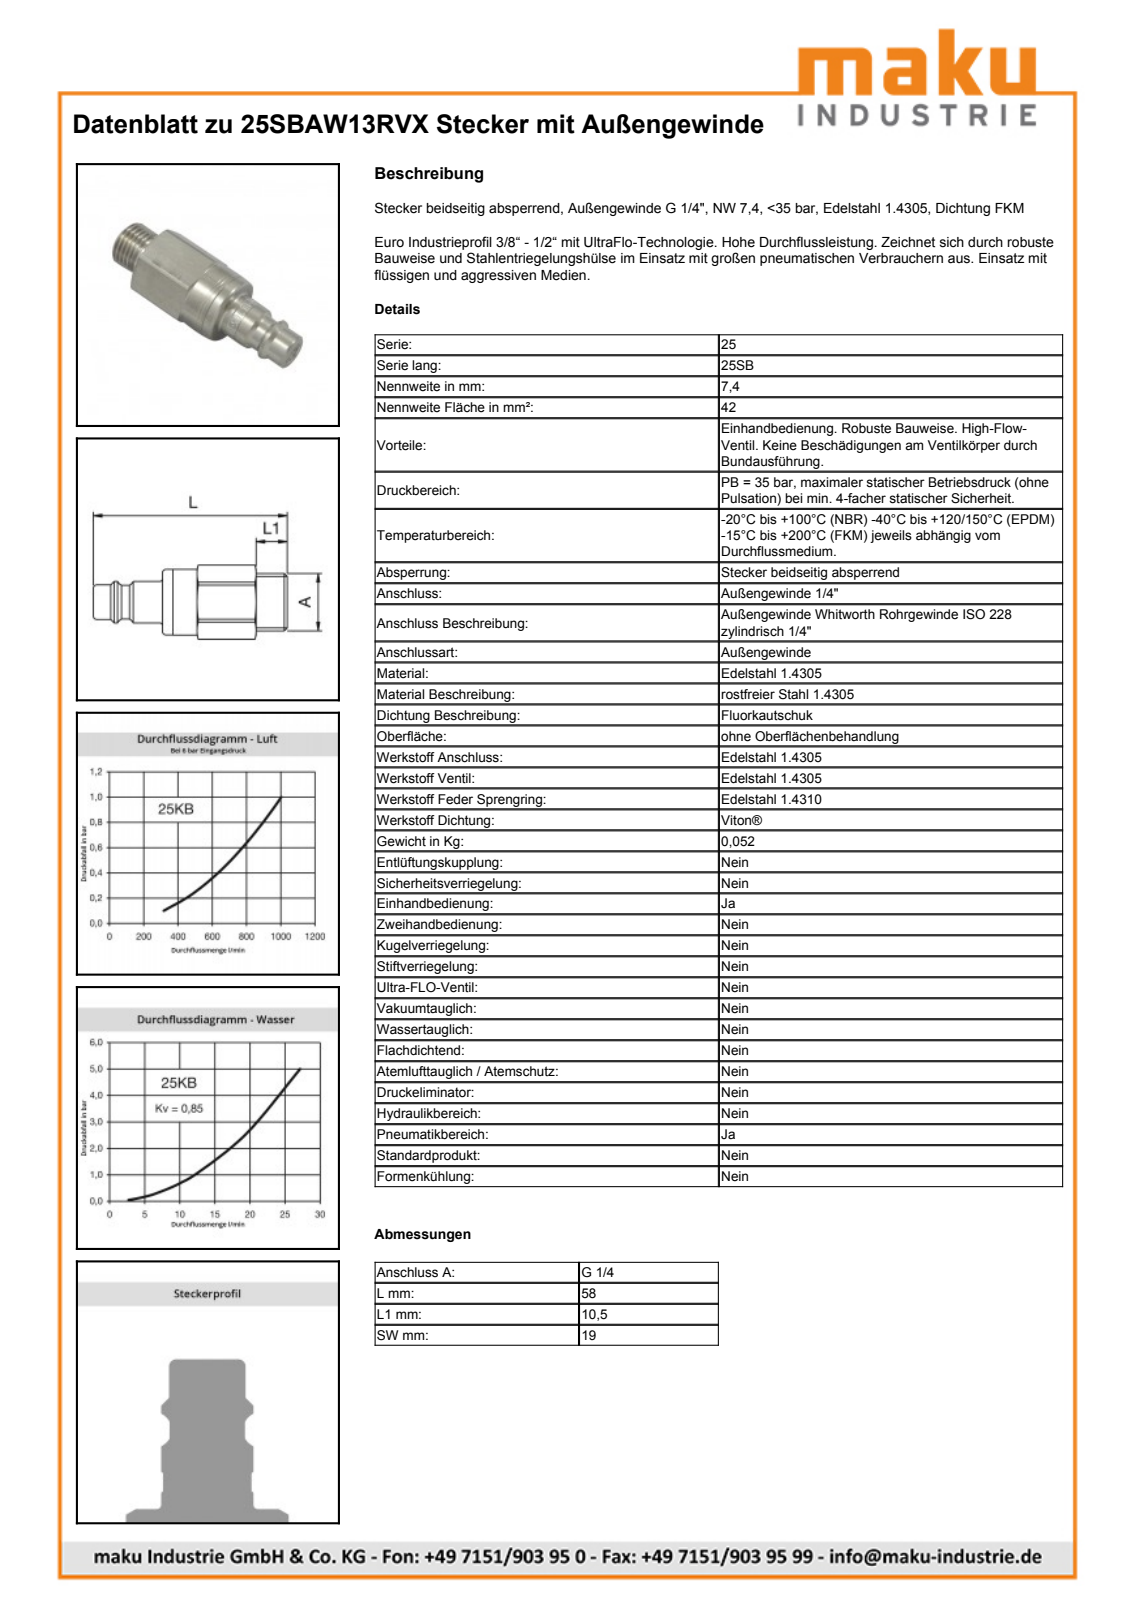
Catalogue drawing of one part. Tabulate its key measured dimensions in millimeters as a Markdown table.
| quantity | value |
| --- | --- |
| part name | D107955 |
| STEP written by | Autodesk Inventor 2013 (AUTOMOTIVE_DESIGN) |
| units | millimeters |
| bodies | 1 solid, 56 faces (16 planar, 19 cylindrical, 21 other) |
| overall size | 58 × 20.96 × 20.84 |
| volume | 11 382 mm³ |
| surface area | 4 196 mm² |
| round holes (diameter × count) | 15.1 × 1, 16 × 1 |
| round bosses / shafts (diameter × count) | 19 × 1, 18.95 × 1, 17 × 1, 14.99 × 1, 13.16 × 1, 12 × 1, 9.9 × 1, 9.75 × 1 |
| partial cylindrical surfaces (radius × count) | 10.7 × 1 |
| main face-to-face distances | 19, 27.5, 20, 10.5, 38, 47.5, 58, 47.1, 27.1, 0.4 |
